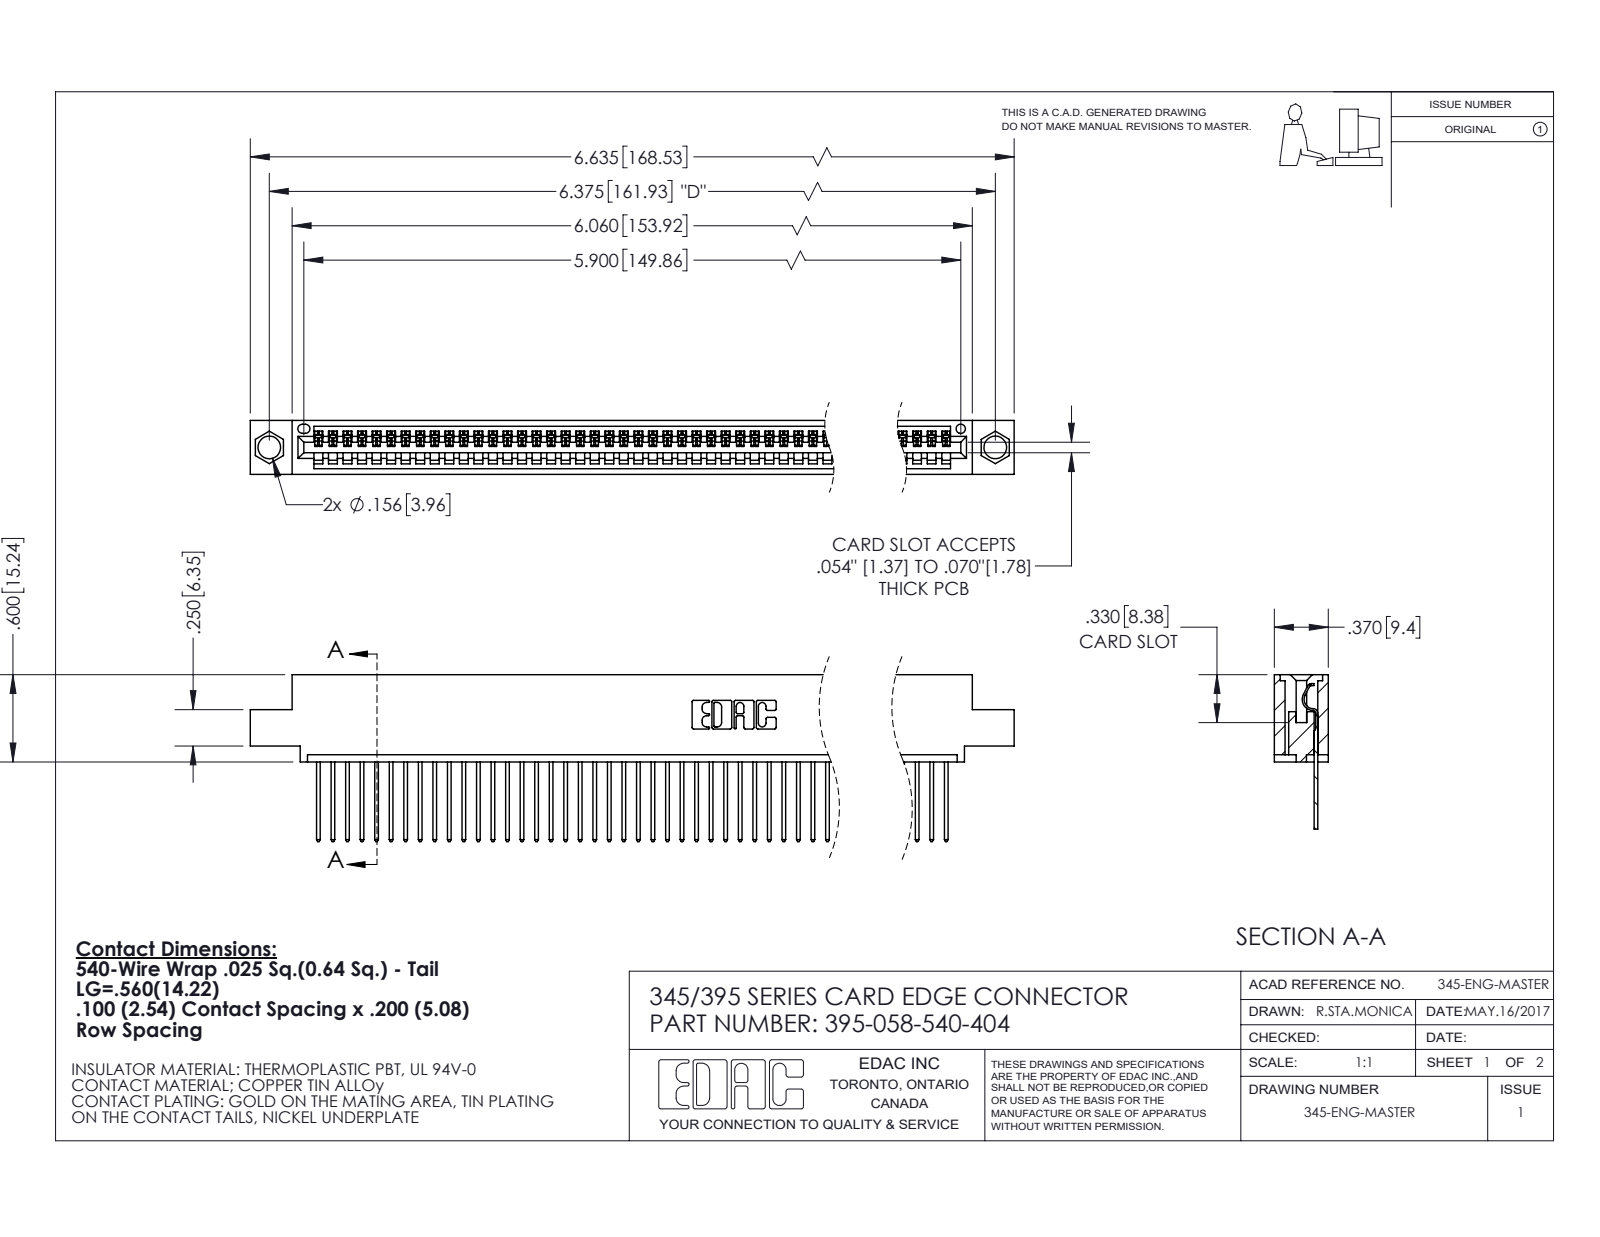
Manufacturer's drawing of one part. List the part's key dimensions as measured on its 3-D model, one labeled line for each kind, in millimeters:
Part name (STEP PRODUCT): 345-292-001_345-293-140; 395-058-540-404; 345 Part_0.110 Offset - 0.156 Dia-TI
STEP written by: SolidWorks 2020 (CONFIG_CONTROL_DESIGN)
Units: millimetres
Bodies: 59 solids, 3508 faces (2418 planar, 1090 cylindrical, 0 other)
Overall size (bounding box): 168.5 × 29.1 × 9.4
Volume: 16 000 mm³ · Surface area: 22 020 mm²
Round holes (diameter × count): ⌀4 ×2, ⌀1.6 ×1
Partial cylindrical surfaces — rounded edges, fillets, slot ends (radius × count): R0.2 ×116, R0.3 ×116, R0.3 ×22, R0.2 ×6, R0.8 ×6, R0.7 ×3, R0.8 ×2, R1 ×2
Main face-to-face distances: 7.6, 1.8, 9.4, 2.5, 6.9, 0.6, 5.1, 5.7, 3.8, 1.8
Hole centre spacings: 6.9, 155.9, 161.9
